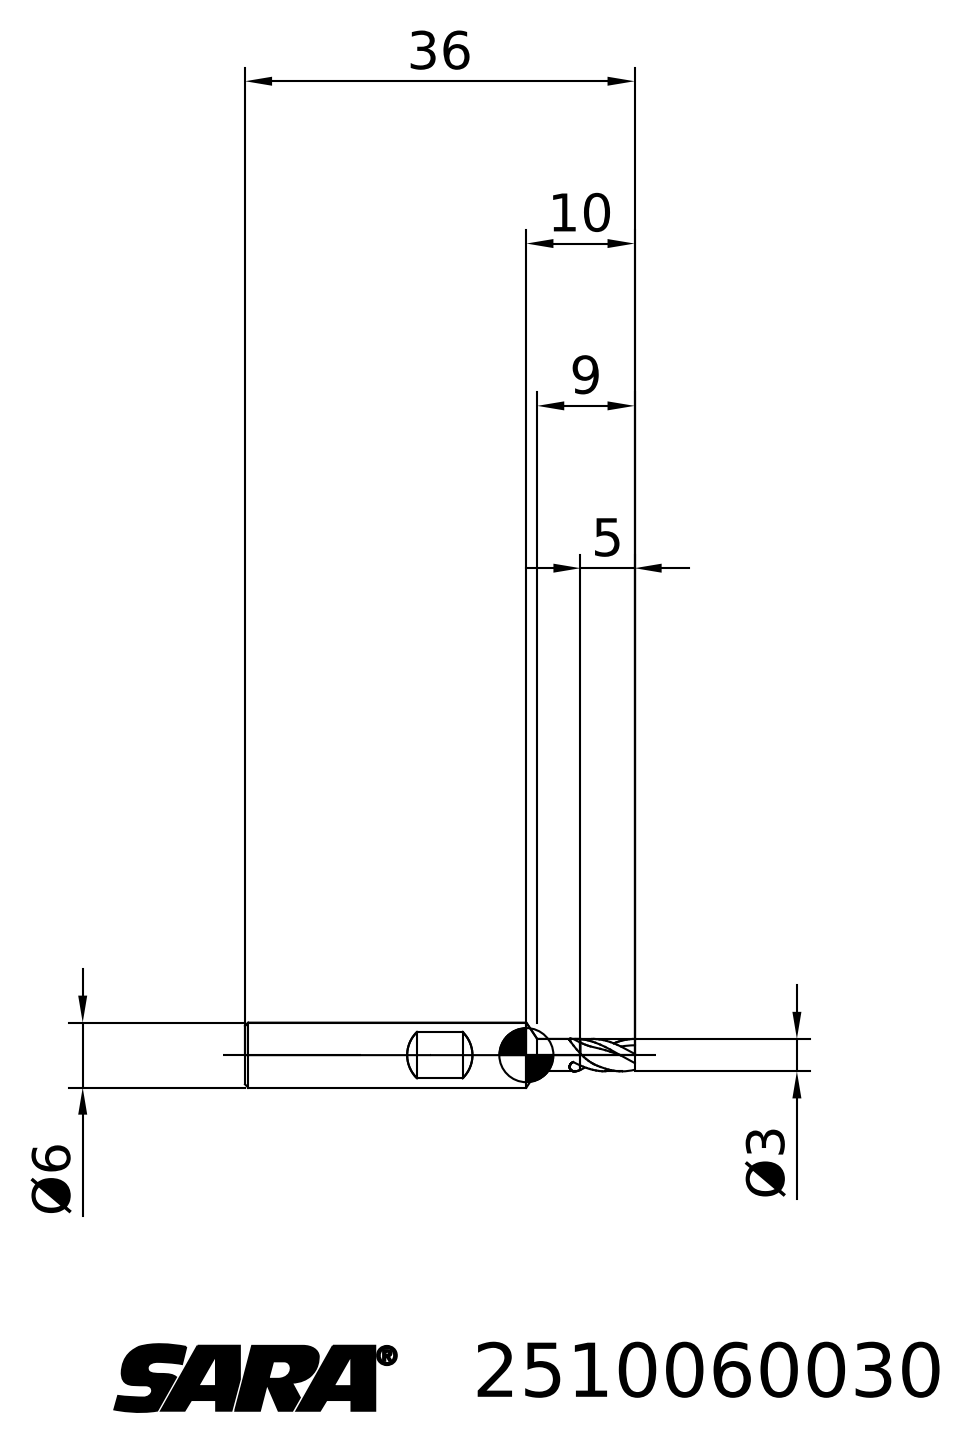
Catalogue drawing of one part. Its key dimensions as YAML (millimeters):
step_written_by: "TDM (AUTOMOTIVE_DESIGN)"
units: millimeters
bodies: {solids: 2, faces: 28, planar: 7, cylindrical: 0, other: 21}
overall_size: [36, 6, 6]
volume: 785
surface_area: 642
face_to_face_distances: [31, 5, 36]
